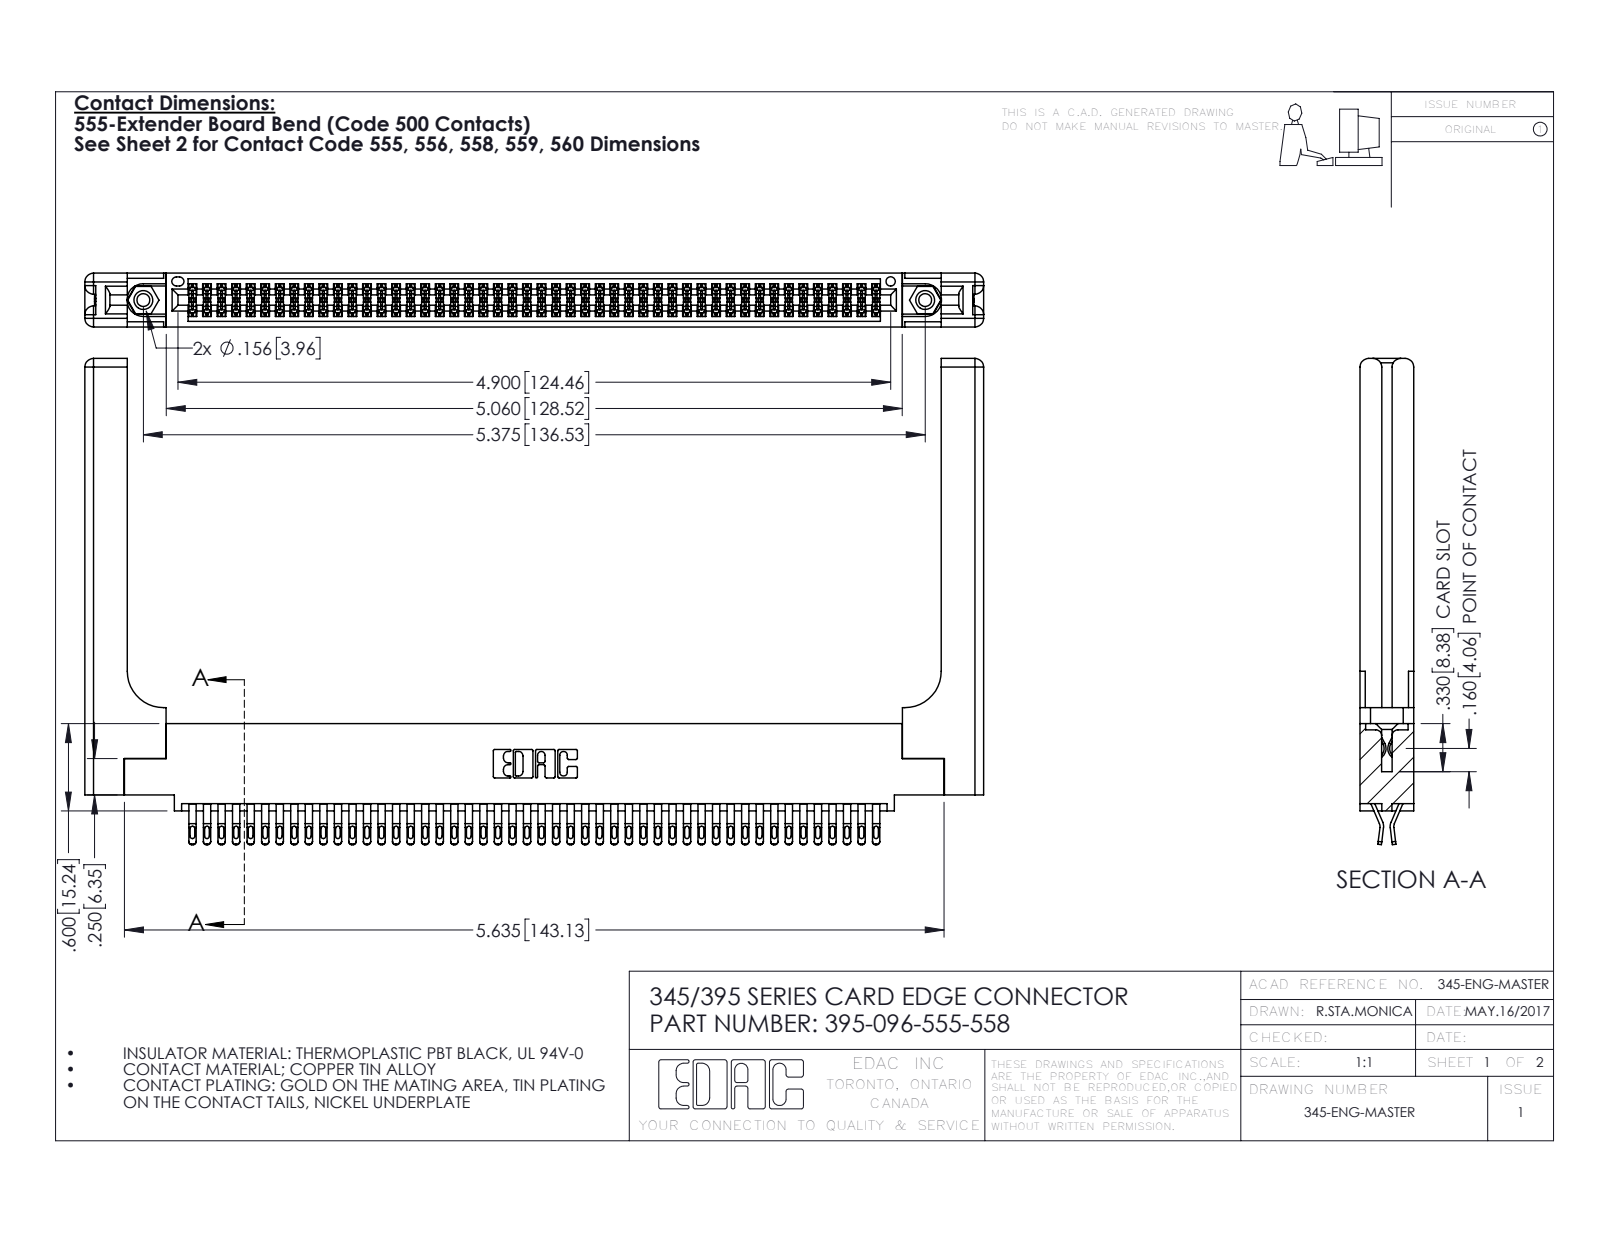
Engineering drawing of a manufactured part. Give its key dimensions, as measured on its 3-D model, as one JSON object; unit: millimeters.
{"part_name": "345-292-001_555 Tail; 395-096-555-558; 345-220-058_345-220-058; 345-250-001_345-250-001-102 (+1 more)", "step_written_by": "SolidWorks 2016 (CONFIG_CONTROL_DESIGN)", "units": "millimeters", "bodies": {"solids": 101, "faces": 5762, "planar": 3208, "cylindrical": 2494, "other": 60}, "overall_size": [156.9, 84.9, 9.4], "volume_mm3": 23970, "surface_area_mm2": 29150, "round_holes": [[2.3, 2], [3.2, 2], [4, 2], [1.6, 1]], "round_bosses_or_shafts": [[3.9, 2]], "partial_cylinders_radius": [[0.4, 240], [0.5, 192], [0.2, 144], [0.3, 22], [1.5, 16], [0.2, 6], [0.8, 6], [0.7, 3]], "face_to_face_distances": [1.8, 9.4, 7.6, 0.6, 2.5, 6.9, 5.1, 5.7, 3.8, 3.8], "hole_center_spacings": [6.9, 130.5, 136.5]}
